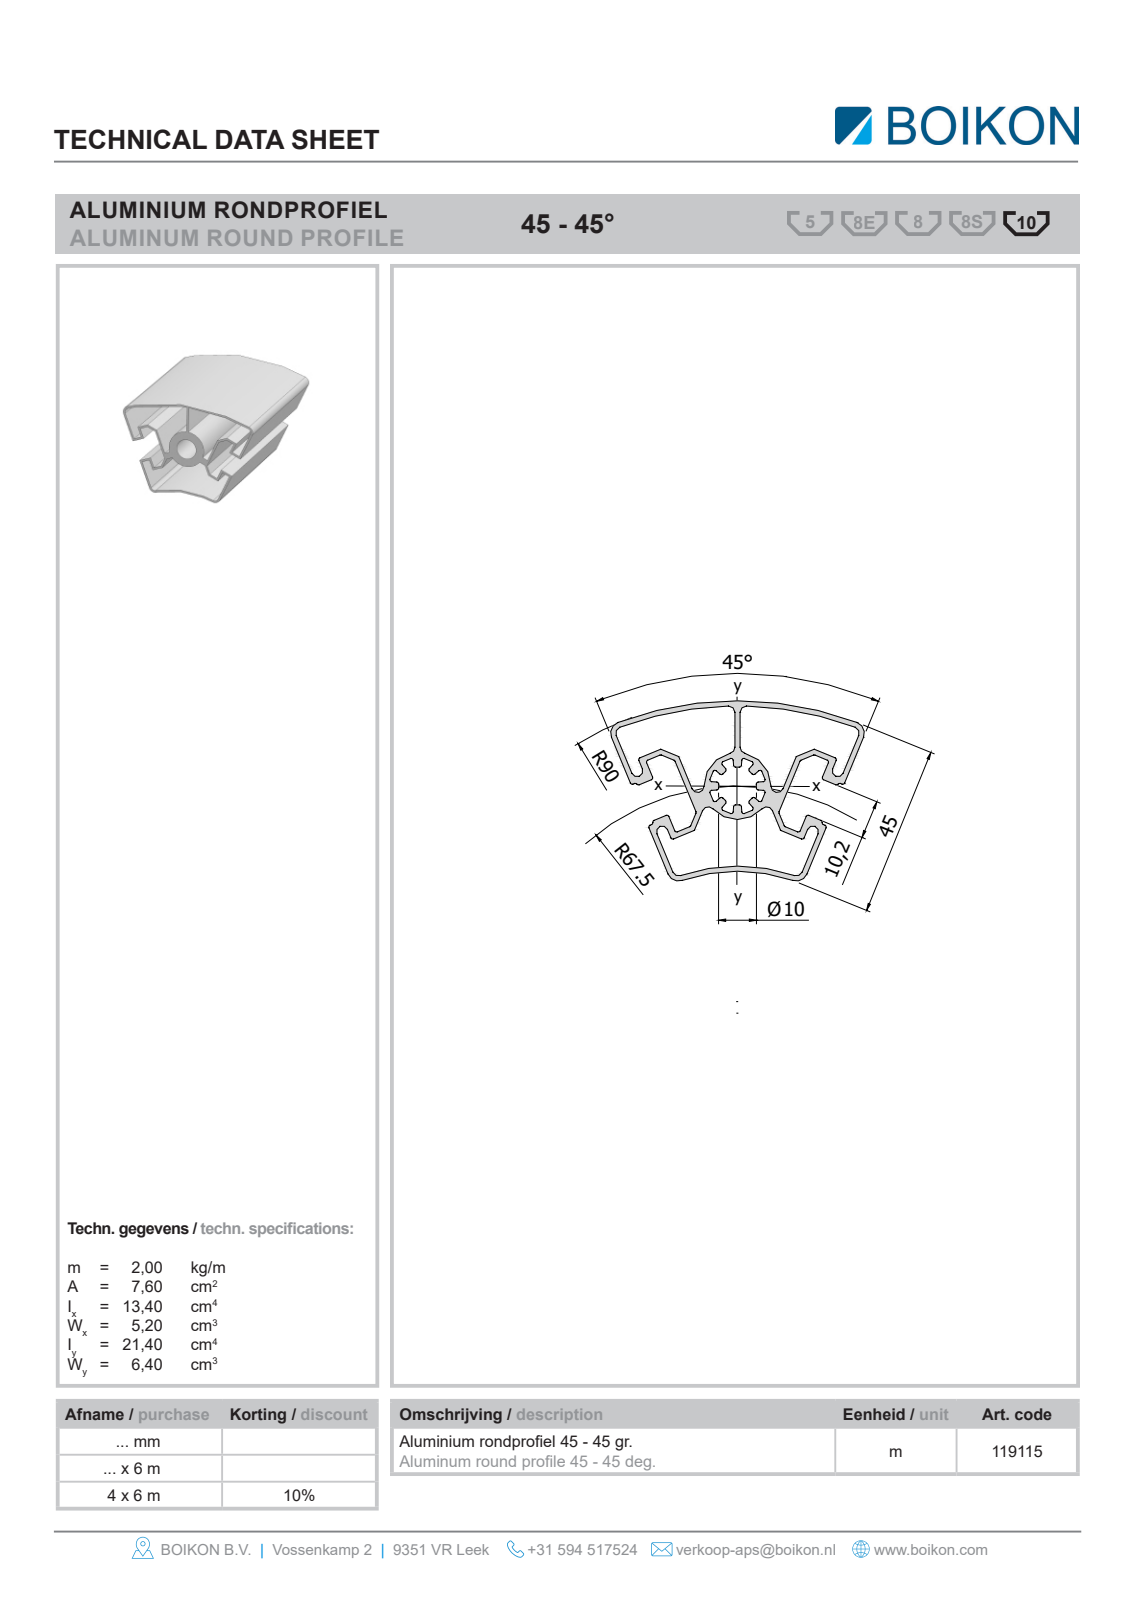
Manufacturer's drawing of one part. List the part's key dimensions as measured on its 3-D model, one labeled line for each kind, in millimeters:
Part name (STEP PRODUCT): Root; 119115Rondprofiel 45-45gr.BOIKON0
STEP written by: HiCAD 2013 1802.4 Build 509 (AUTOMOTIVE_DESIGN)
Units: millimetres
Bodies: 1 solid, 109 faces (73 planar, 36 cylindrical, 0 other)
Overall size (bounding box): 1000 × 62.36 × 56.95
Volume: 735 004 mm³ · Surface area: 687 892 mm²
Partial cylindrical surfaces — rounded edges, fillets, slot ends (radius × count): R1 ×7, R3 ×4, R2 ×1, R5 ×1, R8 ×1, R10 ×1, R45 ×1, R47 ×1
Main face-to-face distances: 2, 10.5, 12.5, 4, 8.5, 17.15, 4.95, 6.5, 6, 14.5
